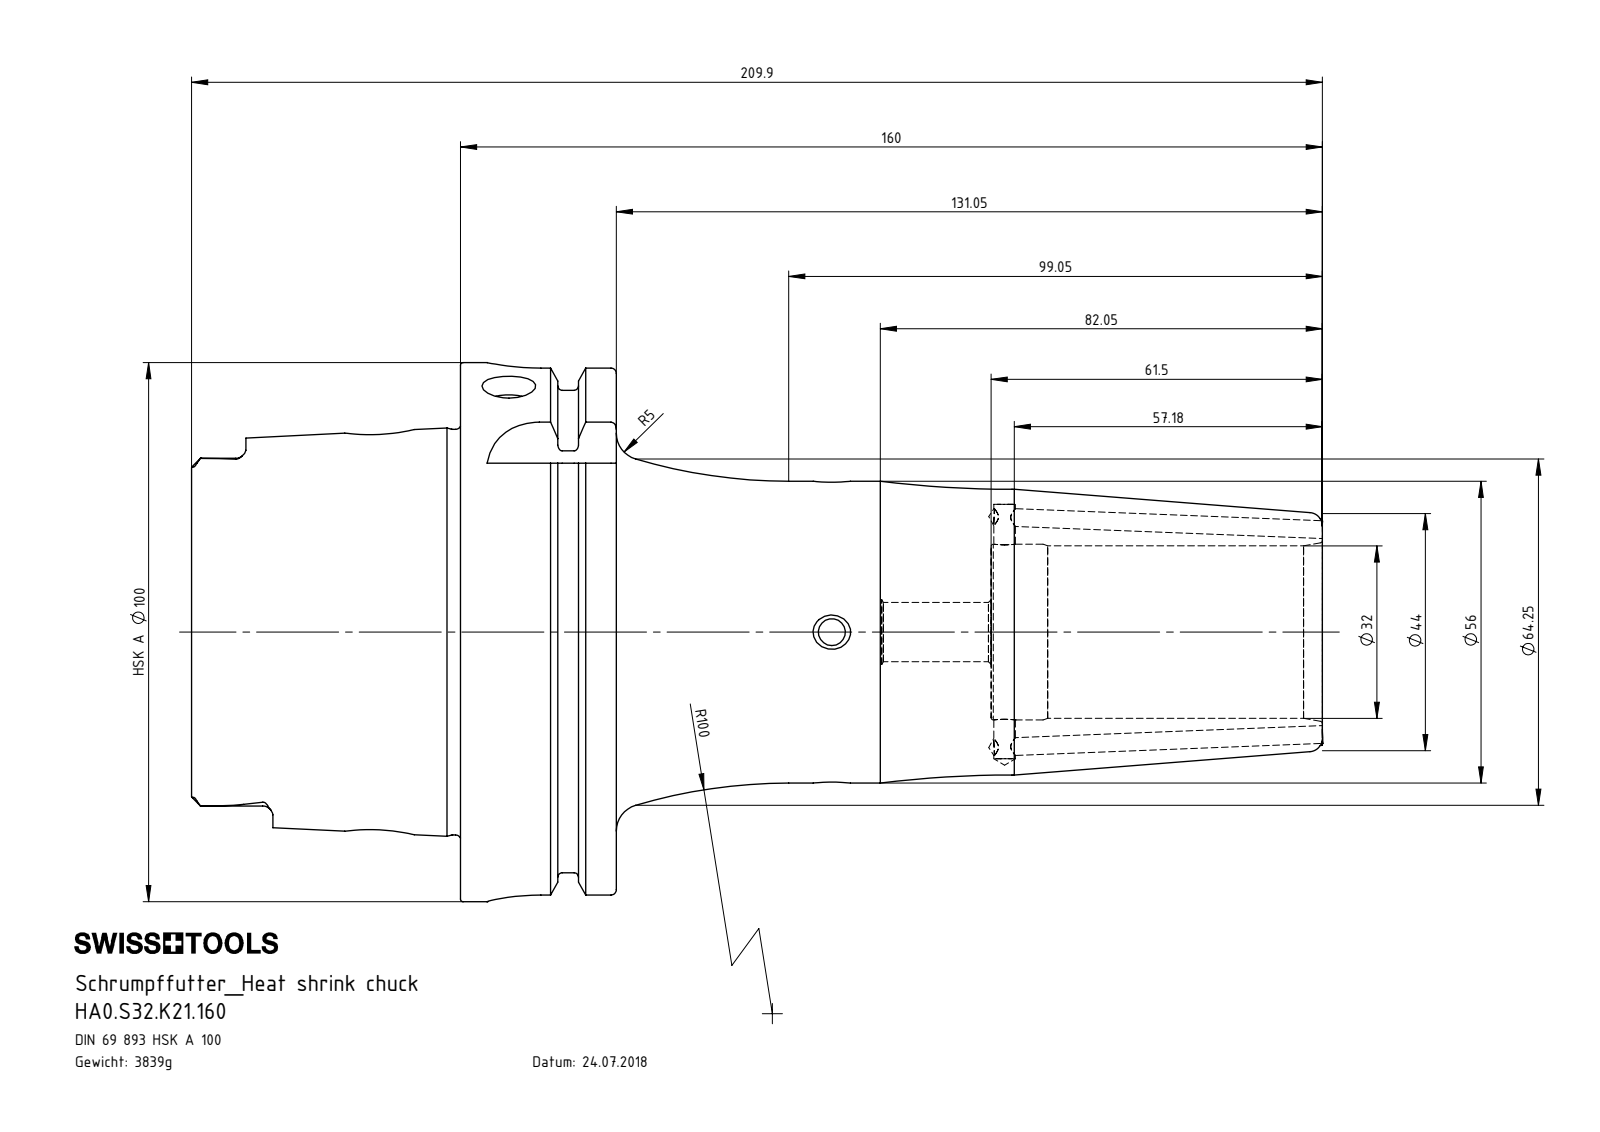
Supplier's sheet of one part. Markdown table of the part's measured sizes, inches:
| quantity | value |
| --- | --- |
| part name | HA0.S32.K21.160; ERU-AN5.K01.020_A; ERU-CJ3.001.008; HA0-S32.K21.160_C_Fertigbearbeitung |
| STEP written by | SolidWorks 2017 (CONFIG_CONTROL_DESIGN) |
| units | inches |
| bodies | 4 solids, 303 faces (95 planar, 86 cylindrical, 122 other) |
| overall size | 8.268 × 3.937 × 3.937 |
| volume | 29.84 in³ |
| surface area | 127 in² |
| round holes (diameter × count) | 0.394 × 3, 0.13 × 2, 0.197 × 2, 0.472 × 2, 0.157 × 1, 0.236 × 1, 0.433 × 1, 0.886 × 1, 1.024 × 1, 1.26 × 1, 1.283 × 1, 2.087 × 1 |
| round bosses / shafts (diameter × count) | 0.157 × 2, 3.937 × 1, 3.62 × 1, 2.963 × 1, 2.205 × 1 |
| partial cylindrical surfaces (radius × count) | 0.075 × 6, 0.192 × 4, 0.394 × 4 |
| main face-to-face distances | 1.14, 0.49, 0.65, 1.965, 2.455, 3.104, 5.843, 3.878, 3.388, 2.738 |
| hole center spacings | 1.262, 2.439, 3.305, 4.567 |
